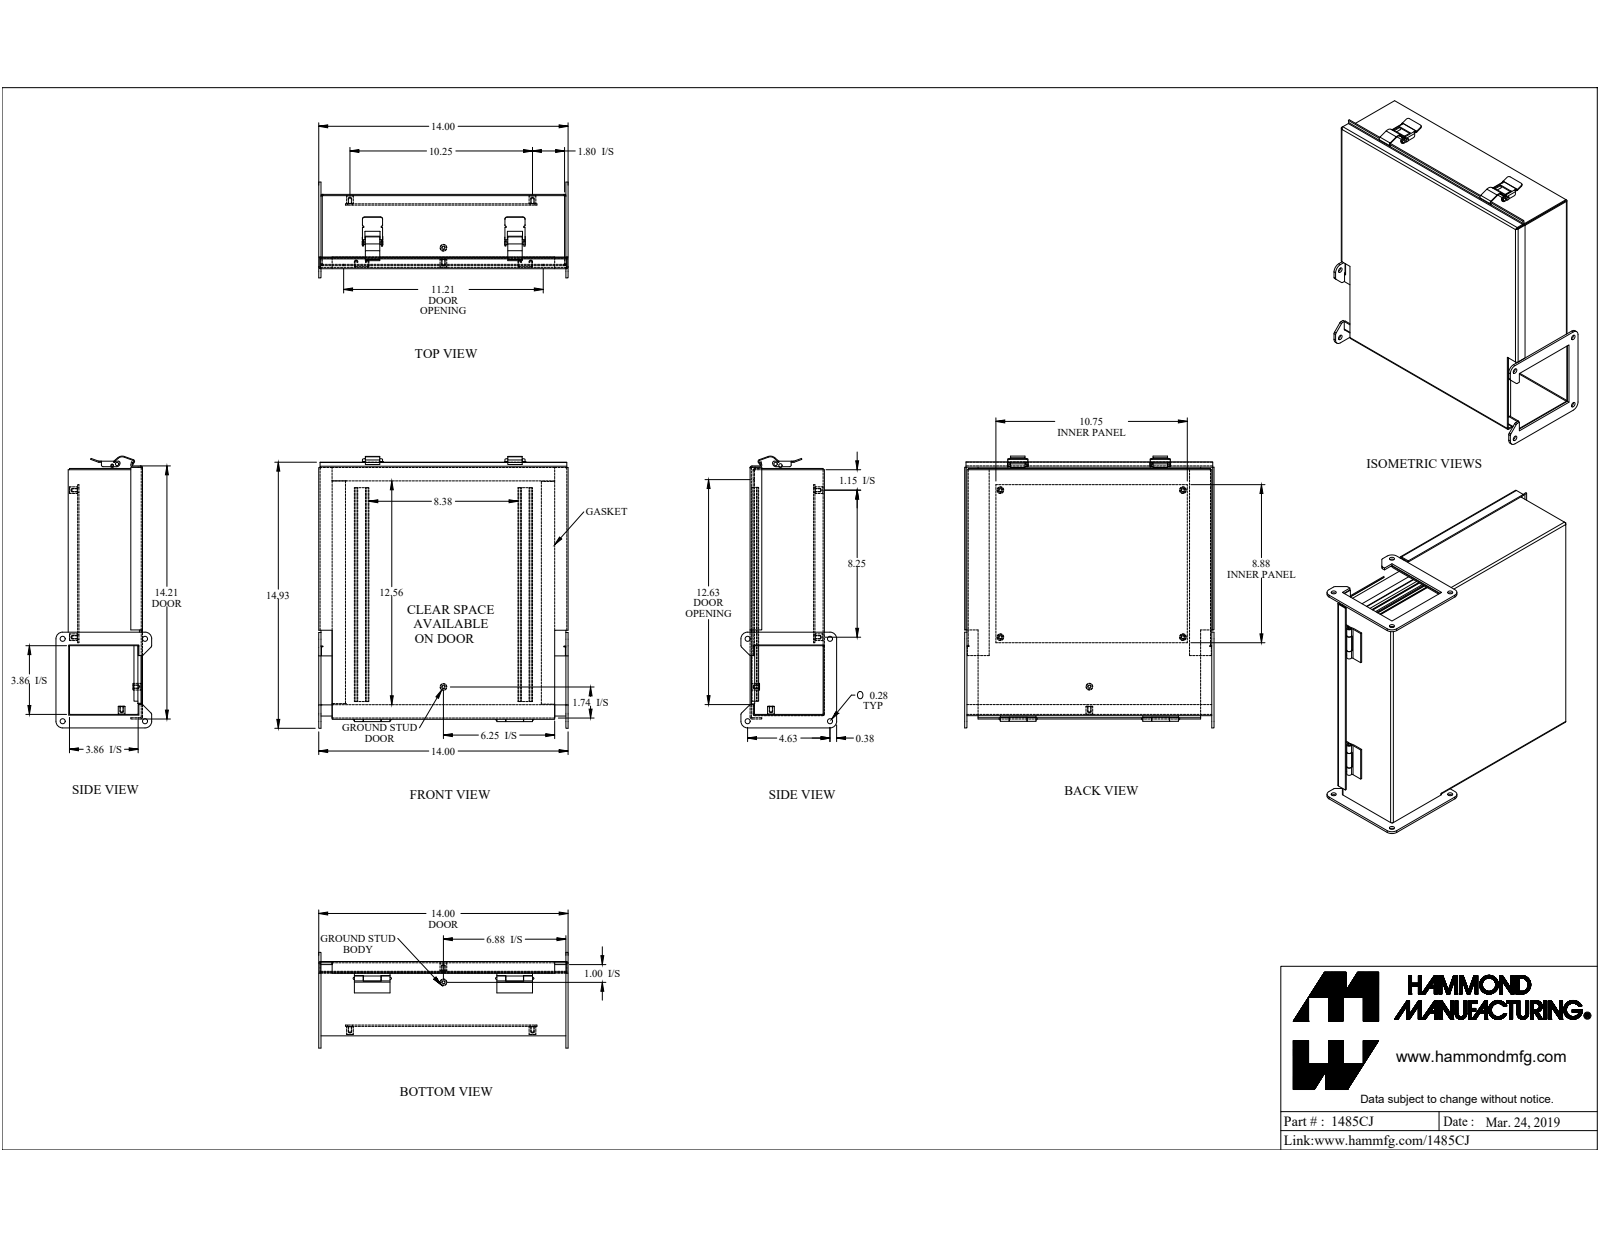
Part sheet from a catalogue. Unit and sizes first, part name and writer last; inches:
Units: inches
Overall size (bounding box): 15.258 × 14 × 5.375
Round holes (diameter × count): ⌀0.156 ×6, ⌀0.265 ×4, ⌀0.281 ×4, ⌀0.125 ×1, ⌀0.13 ×1, ⌀0.164 ×1
Round bosses / shafts (diameter × count): ⌀0.375 ×6, ⌀0.187 ×2, ⌀0.275 ×1, ⌀0.156 ×1, ⌀0.125 ×1
Partial cylindrical surfaces — rounded edges, fillets, slot ends (radius × count): R0.016 ×13, R0.036 ×12, R0.043 ×12, R0.081 ×12, R0.108 ×12, R0.125 ×9, R0.035 ×5, R0.039 ×5
Main face-to-face distances: 0.072, 4.1, 0.532, 3.568, 4.028, 4.172, 13.803, 0.46, 3.64, 0.604
Hole centre spacings: 4.625, 4.625, 6.541, 8.25, 10.25, 13.158, 0.285, 1.098
Volume: 64.97 in³ · Surface area: 1 749 in²
Bodies: 30 solids, 580 faces (352 planar, 206 cylindrical, 22 other)
Part name (STEP PRODUCT): 1485CJ
STEP written by: SolidWorks 2019 (CONFIG_CONTROL_DESIGN)
